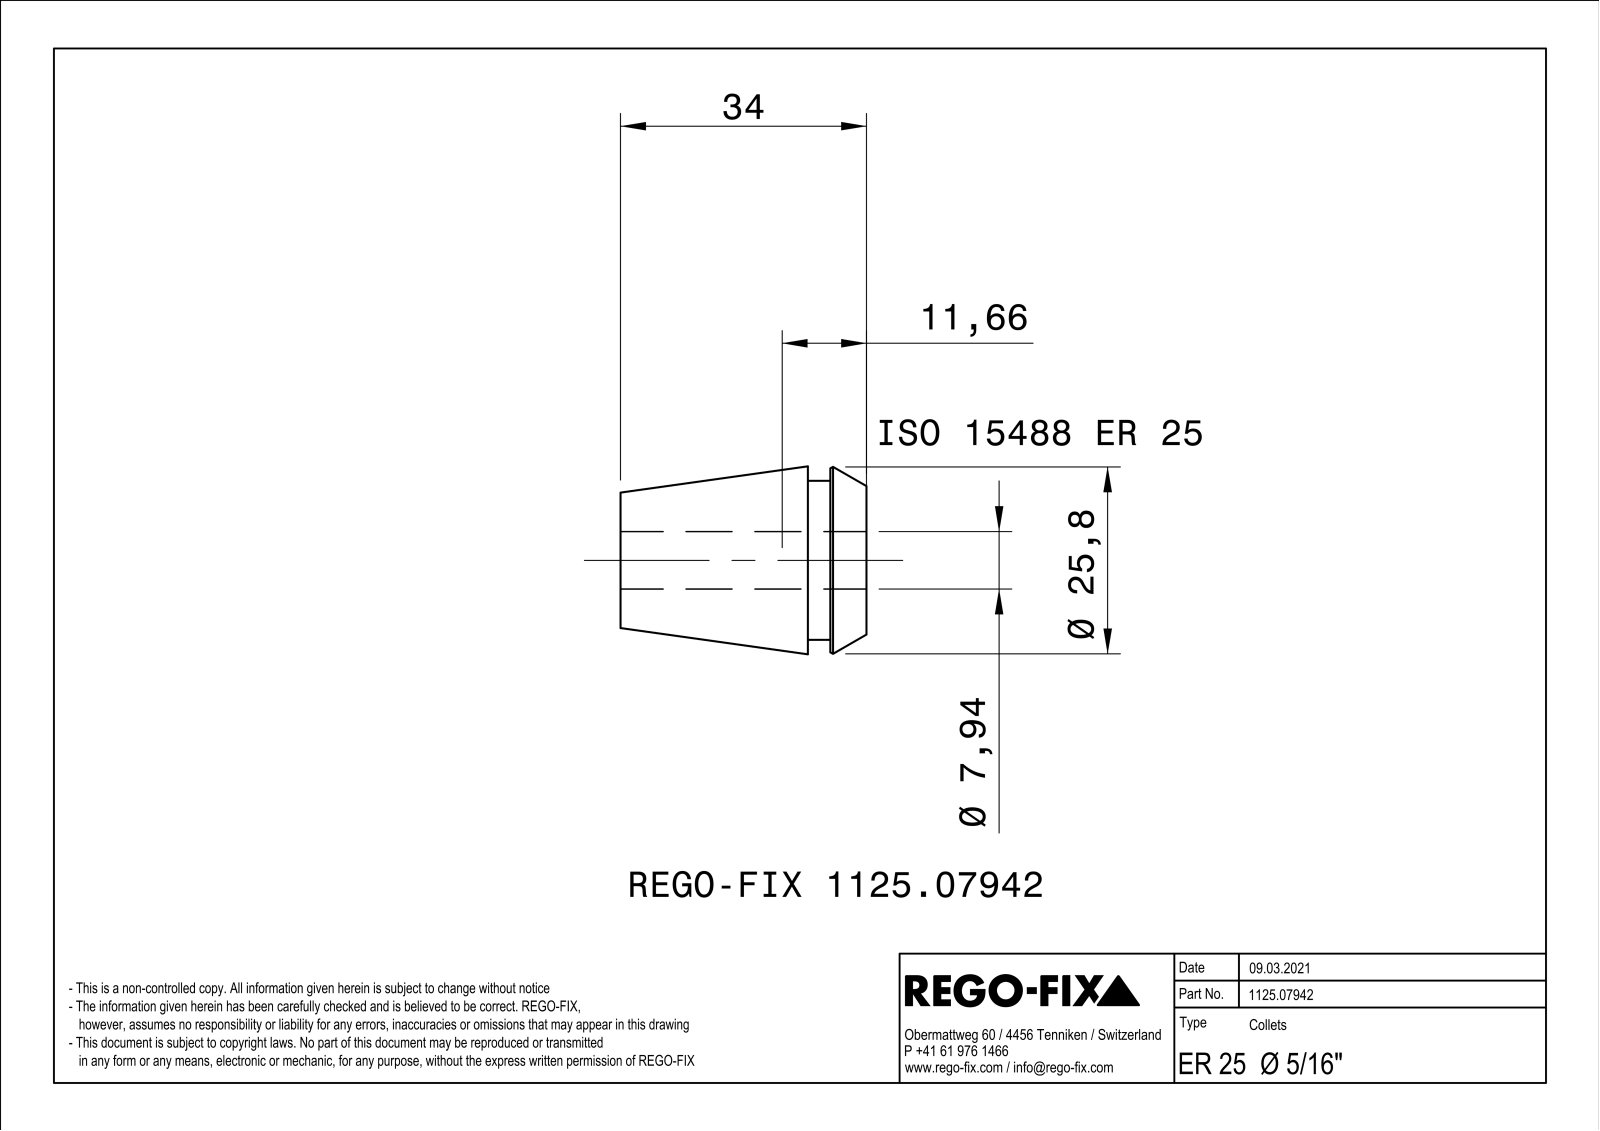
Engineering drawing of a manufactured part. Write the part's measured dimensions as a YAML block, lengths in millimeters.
part_name: "NOCUT"
step_written_by: "SIEMENS PLM Software Solid Edge ST10 (AUTOMOTIVE_DESIGN)"
units: millimeters
bodies: {solids: 1, faces: 177, planar: 72, cylindrical: 25, other: 80}
overall_size: [34, 25.99, 25.99]
volume: 9132
surface_area: 10236
round_holes:
  - {diameter: 7.94, count: 1}
round_bosses_or_shafts:
  - {diameter: 22, count: 1}
partial_cylinders:
  - {radius: 0.4, count: 8}
face_to_face_distances: [0.8, 34, 8.1, 25.9, 5, 3.1, 29]
